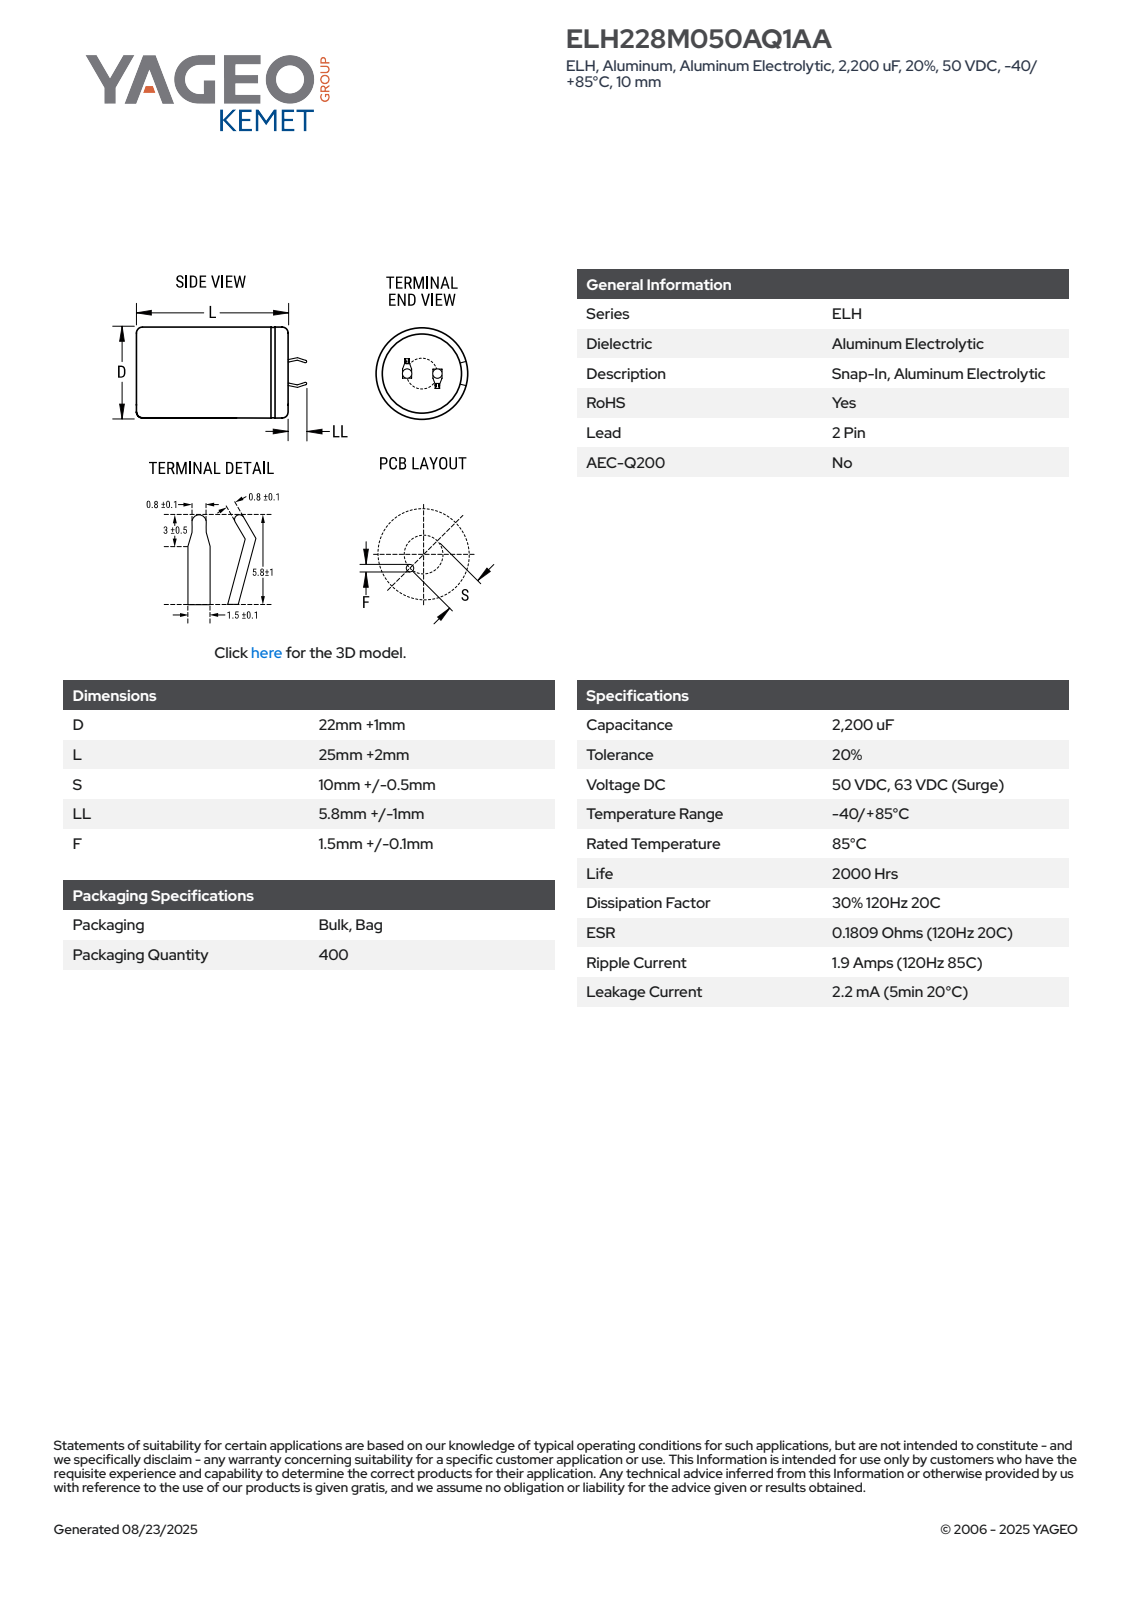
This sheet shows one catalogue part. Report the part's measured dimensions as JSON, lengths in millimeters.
{"part_name": "CARS_K2P_22X25_D23L27S10LL6.8F1.6", "step_written_by": "SolidWorks 2014 (AUTOMOTIVE_DESIGN)", "units": "millimeters", "bodies": {"solids": 1, "faces": 100, "planar": 52, "cylindrical": 9, "other": 39}, "overall_size": [33.79, 23, 23], "volume_mm3": 11088, "surface_area_mm2": 2806, "round_holes": [[20.35, 1]], "round_bosses_or_shafts": [[23, 1]], "partial_cylinders_radius": [[11.49, 1]], "face_to_face_distances": [26.99, 27.49, 0.5, 0.6, 7.08, 0.75, 1.35, 7.68, 6.48, 8.23]}
